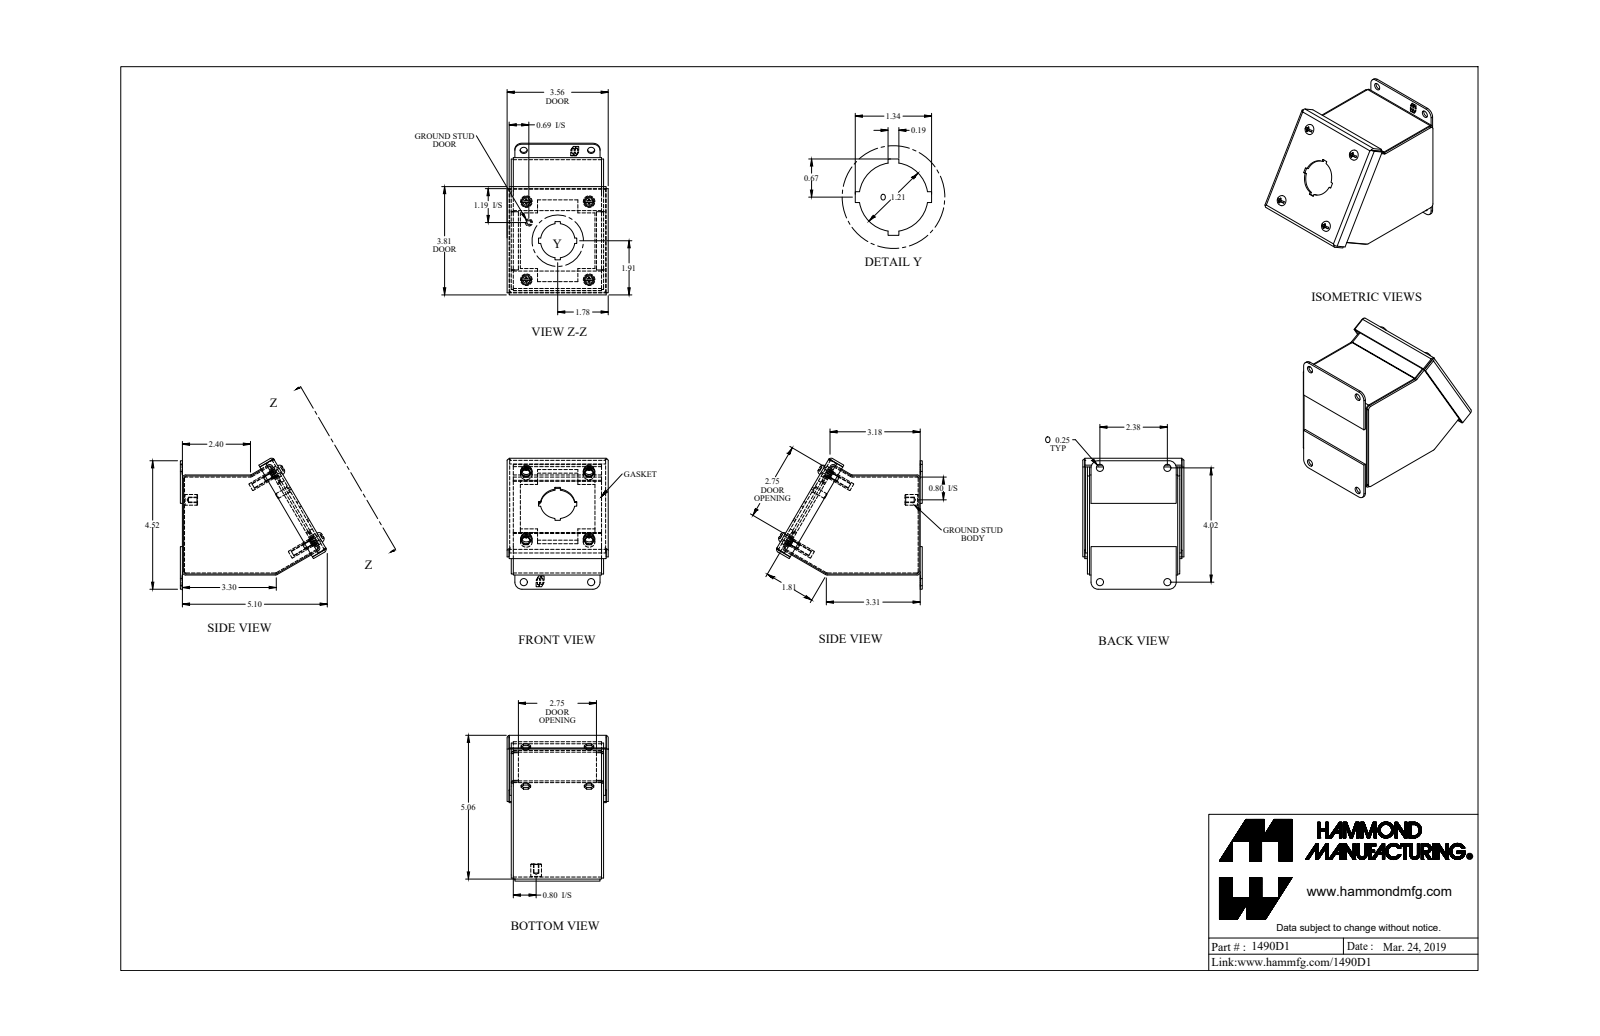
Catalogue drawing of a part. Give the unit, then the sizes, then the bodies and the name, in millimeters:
Units: millimetres
Overall size (bounding box): 130.4 × 117.2 × 90.5
Round holes (diameter × count): ⌀6.4 ×8, ⌀4 ×4, ⌀10.3 ×4, ⌀4 ×1, ⌀30.7 ×1
Round bosses / shafts (diameter × count): ⌀9.9 ×4, ⌀7 ×4, ⌀4.8 ×4, ⌀3.8 ×4, ⌀9.5 ×1, ⌀6.4 ×1, ⌀4.8 ×1
Partial cylindrical surfaces — rounded edges, fillets, slot ends (radius × count): R2.7 ×18, R0.9 ×12, R3.2 ×4, R4.1 ×4, R4.3 ×4, R6.4 ×4
Main face-to-face distances: 1.8, 78.9, 87.6, 1.8, 80.7, 82.6, 80.7, 3.7, 85.8, 89.5
Hole centre spacings: 56.1, 56.5, 44.8, 69.9, 0.4, 44.7, 44.9, 60.3
Volume: 140 000 mm³ · Surface area: 148 000 mm²
Bodies: 21 solids, 571 faces (375 planar, 156 cylindrical, 40 other)
Part name (STEP PRODUCT): 1490D1_Default
STEP written by: SolidWorks 2019 (CONFIG_CONTROL_DESIGN)
